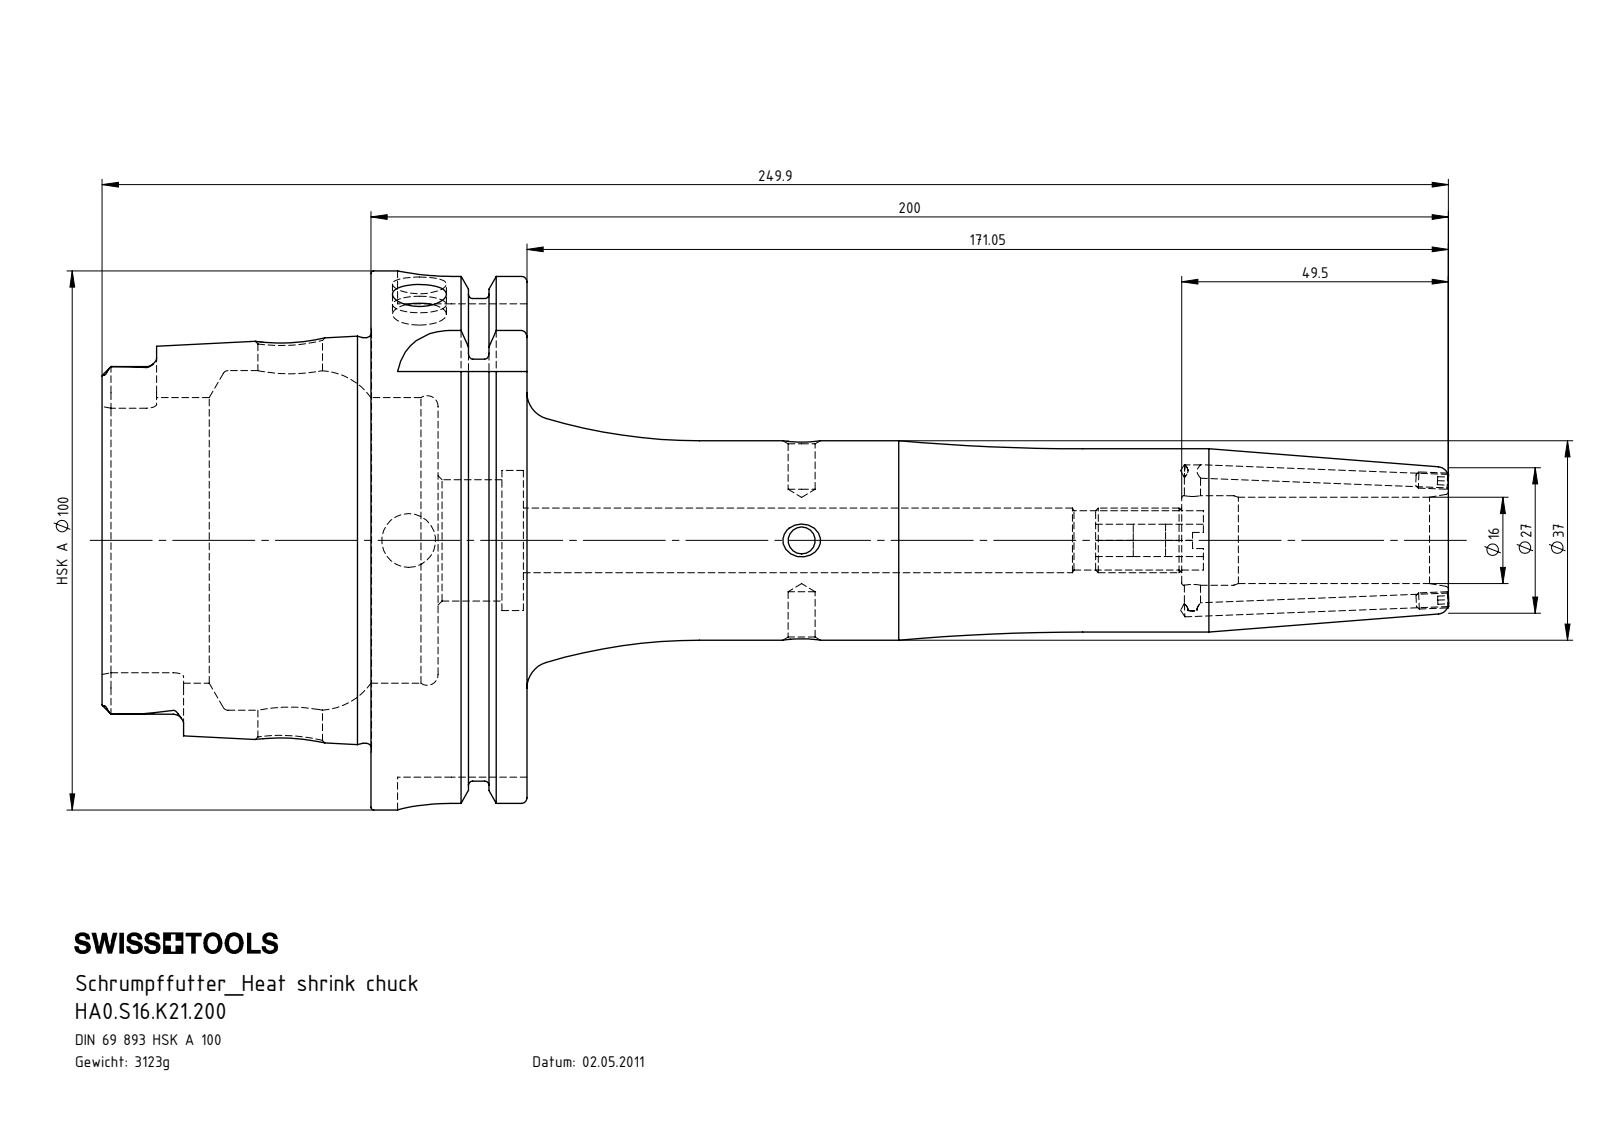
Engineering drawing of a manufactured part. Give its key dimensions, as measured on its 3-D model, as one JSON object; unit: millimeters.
{"part_name": "ERU-AN5.K01.020_A; HA0.S16.K21.200; ERU-CJ2.001.006; HA0-S16.K21.200_C_Fertigbearbeitung", "step_written_by": "SolidWorks 2017 (CONFIG_CONTROL_DESIGN)", "units": "millimeters", "bodies": {"solids": 4, "faces": 307, "planar": 95, "cylindrical": 89, "other": 123}, "overall_size": [249.98, 100, 100], "volume_mm3": 397866, "surface_area_mm2": 77074, "round_holes": [[10, 3], [2.5, 2], [5, 2], [12, 2], [3, 1], [6, 1], [11, 1], [16, 1], [16.6, 1], [22.5, 1], [26, 1], [53, 1]], "round_bosses_or_shafts": [[3, 2], [100, 1], [91.95, 1], [75.26, 1], [37, 1], [34, 1]], "partial_cylinders_radius": [[1.9, 6], [4.88, 4], [10, 4]], "face_to_face_distances": [28.95, 12.45, 16.5, 49.9, 62.35, 78.85, 87.8, 78.2, 28.3, 15.85], "hole_center_spacings": [72.55, 72.95, 94.95, 167.5]}
